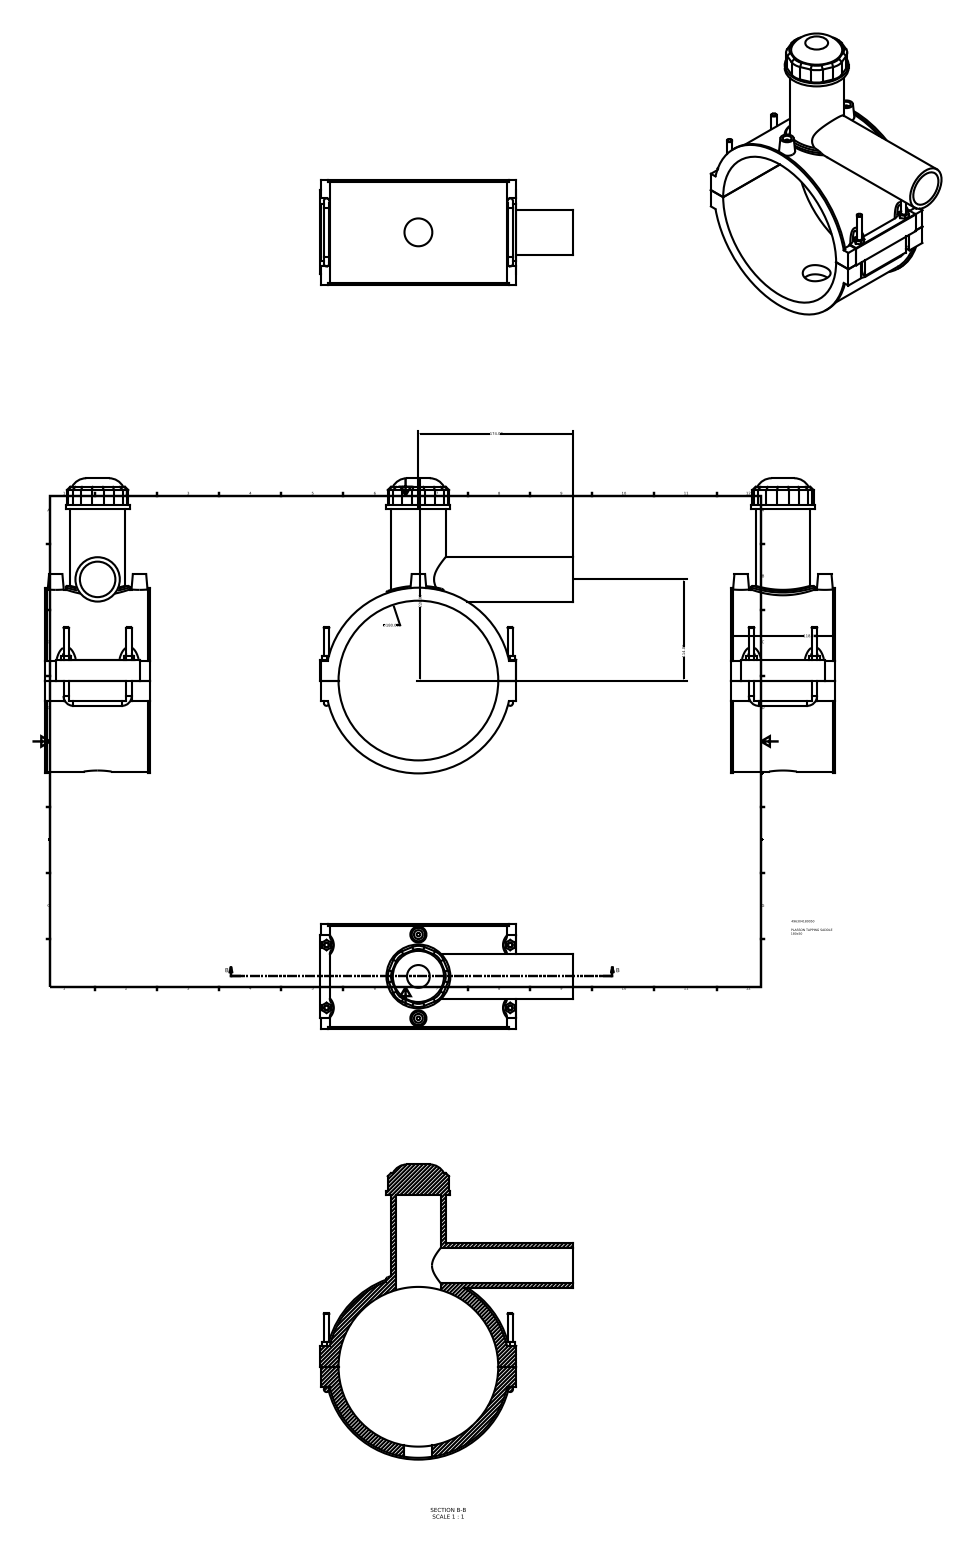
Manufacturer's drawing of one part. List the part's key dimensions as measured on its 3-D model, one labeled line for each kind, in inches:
Part name (STEP PRODUCT): 496304180050
STEP written by: Autodesk Inventor 2015 (AUTOMOTIVE_DESIGN)
Units: inches
Bodies: 1 solid, 181 faces (110 planar, 47 cylindrical, 24 other)
Overall size (bounding box): 13.096 × 11.201 × 4.646
Volume: 77.13 in³ · Surface area: 417.8 in²
Round holes (diameter × count): ⌀0.394 ×2, ⌀1.235 ×1, ⌀1.575 ×1, ⌀1.984 ×1, ⌀7.087 ×1
Round bosses / shafts (diameter × count): ⌀0.236 ×6, ⌀0.157 ×2, ⌀8.24 ×1, ⌀8.079 ×1, ⌀2.835 ×1, ⌀2.409 ×1, ⌀1.969 ×1
Partial cylindrical surfaces — rounded edges, fillets, slot ends (radius × count): R0.709 ×8, R0.118 ×4, R0.295 ×4, R0.02 ×1, R4.201 ×1
Main face-to-face distances: 4.646, 0.039, 8.661, 7.62, 7.616, 8.622, 0.884, 0.888, 0.093, 4.553
Hole centre spacings: 1.858, 3.717
